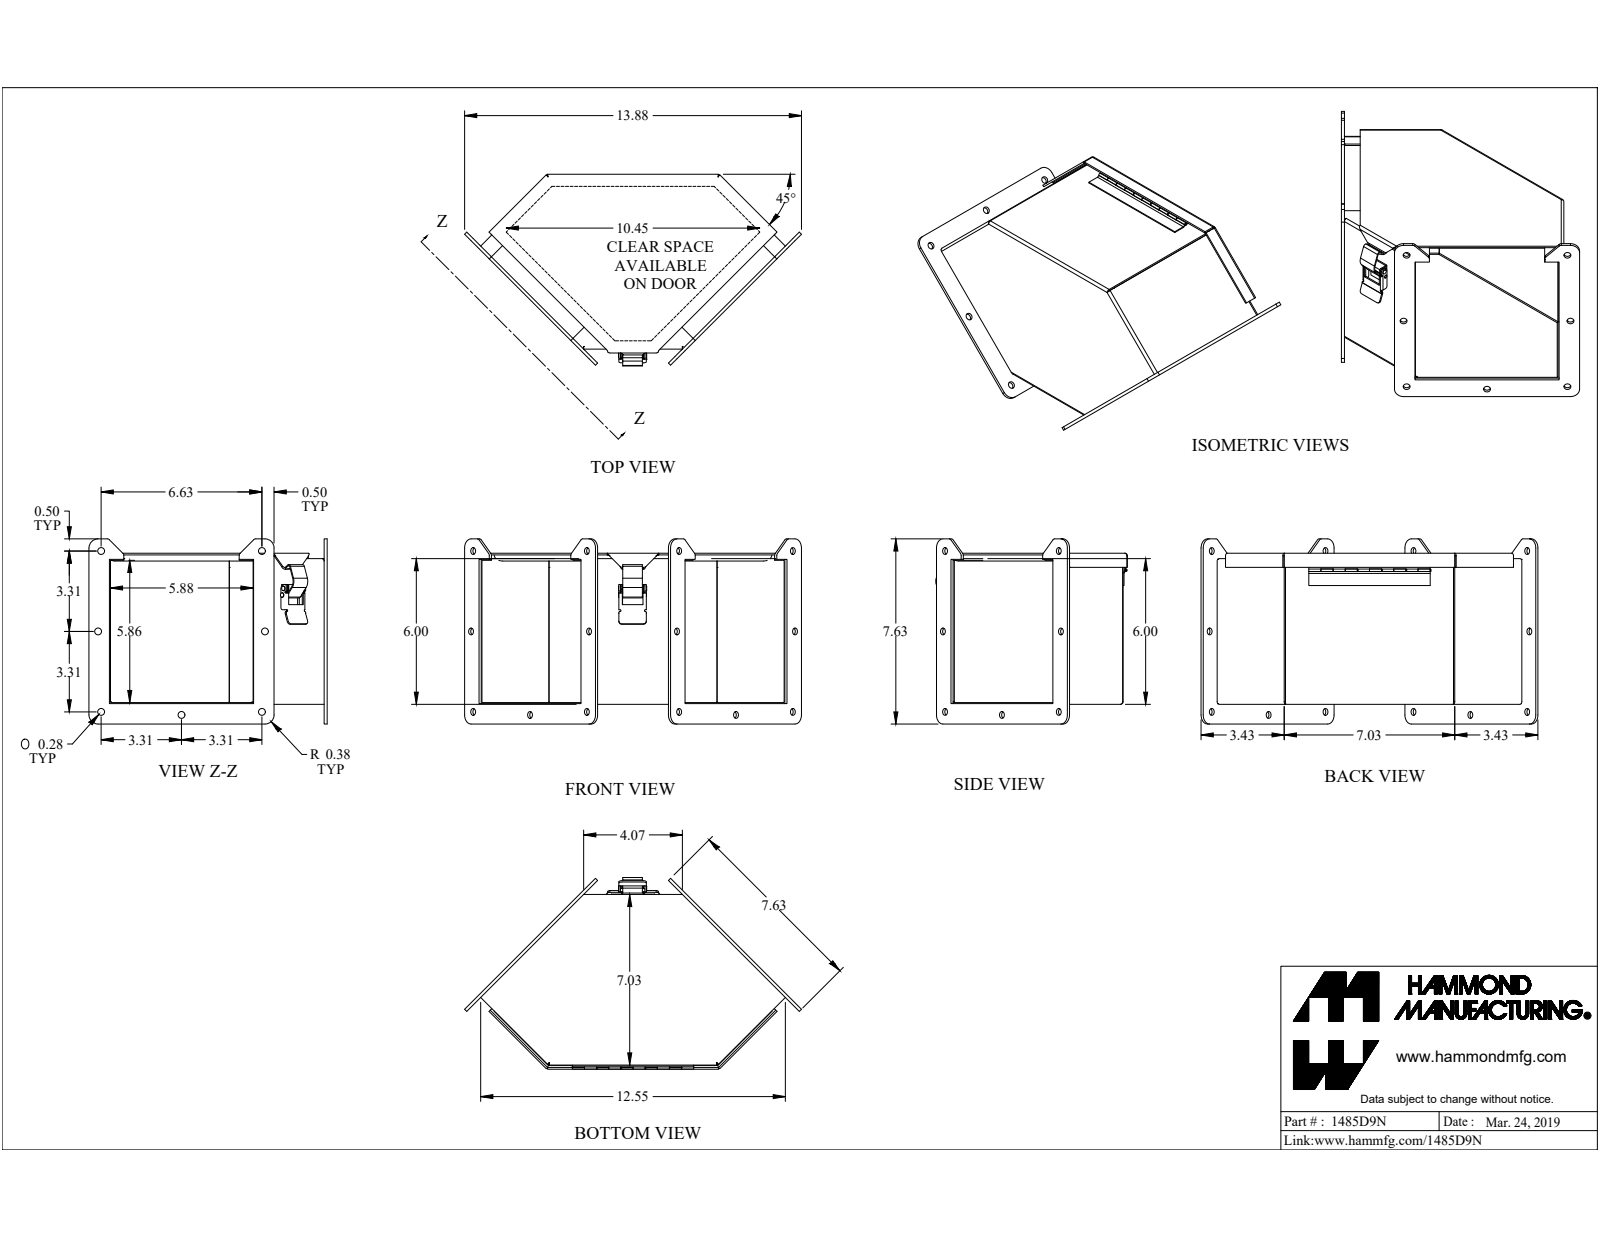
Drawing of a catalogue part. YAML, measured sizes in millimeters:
part_name: "1485D9N"
step_written_by: "SolidWorks 2019 (CONFIG_CONTROL_DESIGN)"
units: millimeters
bodies: {solids: 11, faces: 388, planar: 218, cylindrical: 146, other: 24}
overall_size: [352.5, 200.6, 193.7]
volume: 419800
surface_area: 421700
round_holes:
  - {diameter: 7.1, count: 14}
  - {diameter: 3.3, count: 1}
  - {diameter: 4.2, count: 1}
round_bosses_or_shafts:
  - {diameter: 4.7, count: 2}
  - {diameter: 4, count: 1}
  - {diameter: 3.2, count: 1}
  - {diameter: 2.5, count: 1}
  - {diameter: 1.1, count: 1}
partial_cylinders:
  - {radius: 0.9, count: 13}
  - {radius: 2.7, count: 13}
  - {radius: 3.2, count: 11}
  - {radius: 9.5, count: 8}
  - {radius: 0.4, count: 7}
  - {radius: 6.4, count: 6}
  - {radius: 0.9, count: 3}
  - {radius: 1, count: 3}
face_to_face_distances: [1.8, 156.2, 154.4, 158, 176.6, 1.8, 225.4, 223.6, 228.5, 226.7]
hole_center_spacings: [84.2, 191, 84.2, 123.5, 168.3, 168.3, 191, 238]
